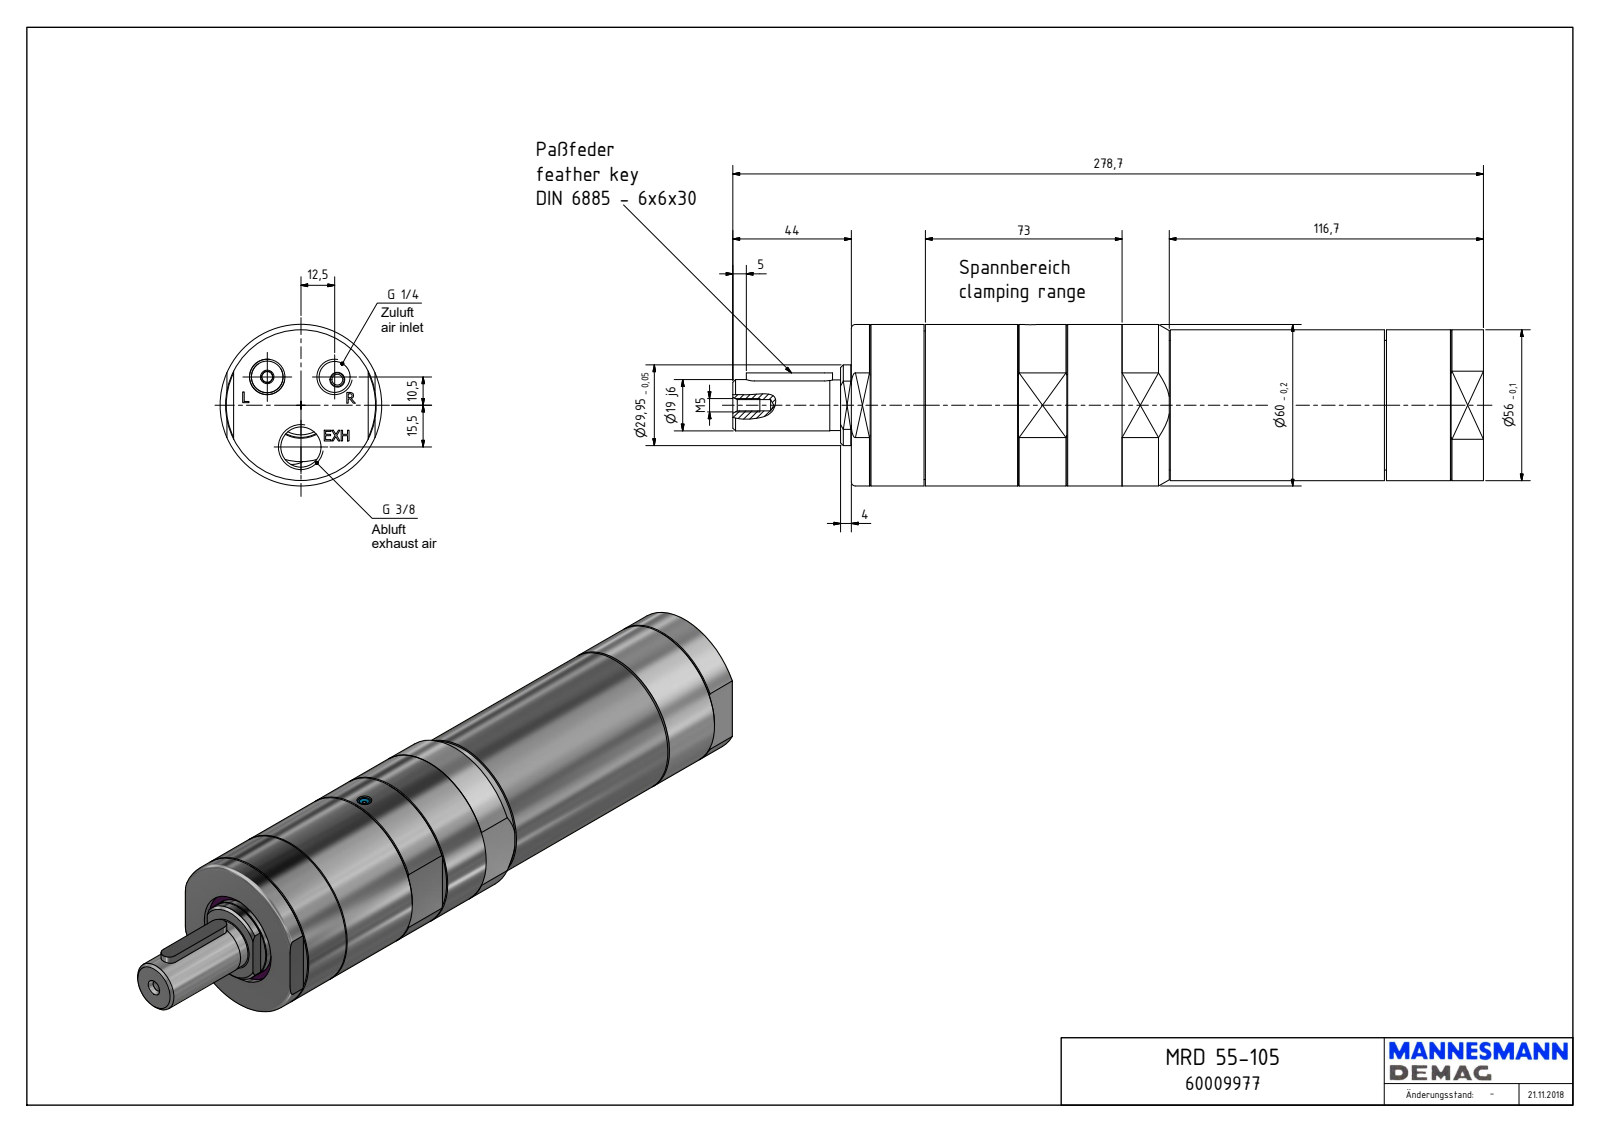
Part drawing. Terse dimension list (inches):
name: MRD 55-105_60009977
written by: Autodesk Inventor 2018 (AUTOMOTIVE_DESIGN)
unit: in
bodies: 1 solid, 226 faces (125 planar, 47 cylindrical, 54 other)
size: 10.972 × 2.362 × 2.362
volume: 38.1 in³; area: 92.88 in²
holes: 2× ⌀0.157, 1× ⌀0.061, 1× ⌀0.163, 1× ⌀0.217, 1× ⌀0.451, 1× ⌀0.589, 1× ⌀1.378, 1× ⌀1.437, 1× ⌀1.575, 1× ⌀1.905, 1× ⌀2.18
bosses: 1× ⌀2.362, 1× ⌀2.205, 1× ⌀2.172, 1× ⌀1.897, 1× ⌀1.179, 1× ⌀0.748, 1× ⌀0.74, 1× ⌀0.197
rounds: 2× R0.118, 2× R0.236, 1× R0.225, 1× R0.81, 1× R0.906, 1× R1.042
face distances: 9.24, 2.165, 0.098, 2.067, 7.791, 1.449, 4.661, 3.13, 4.579, 0.031
hole spacings: 0.643, 1.136, 0.61, 0.984
